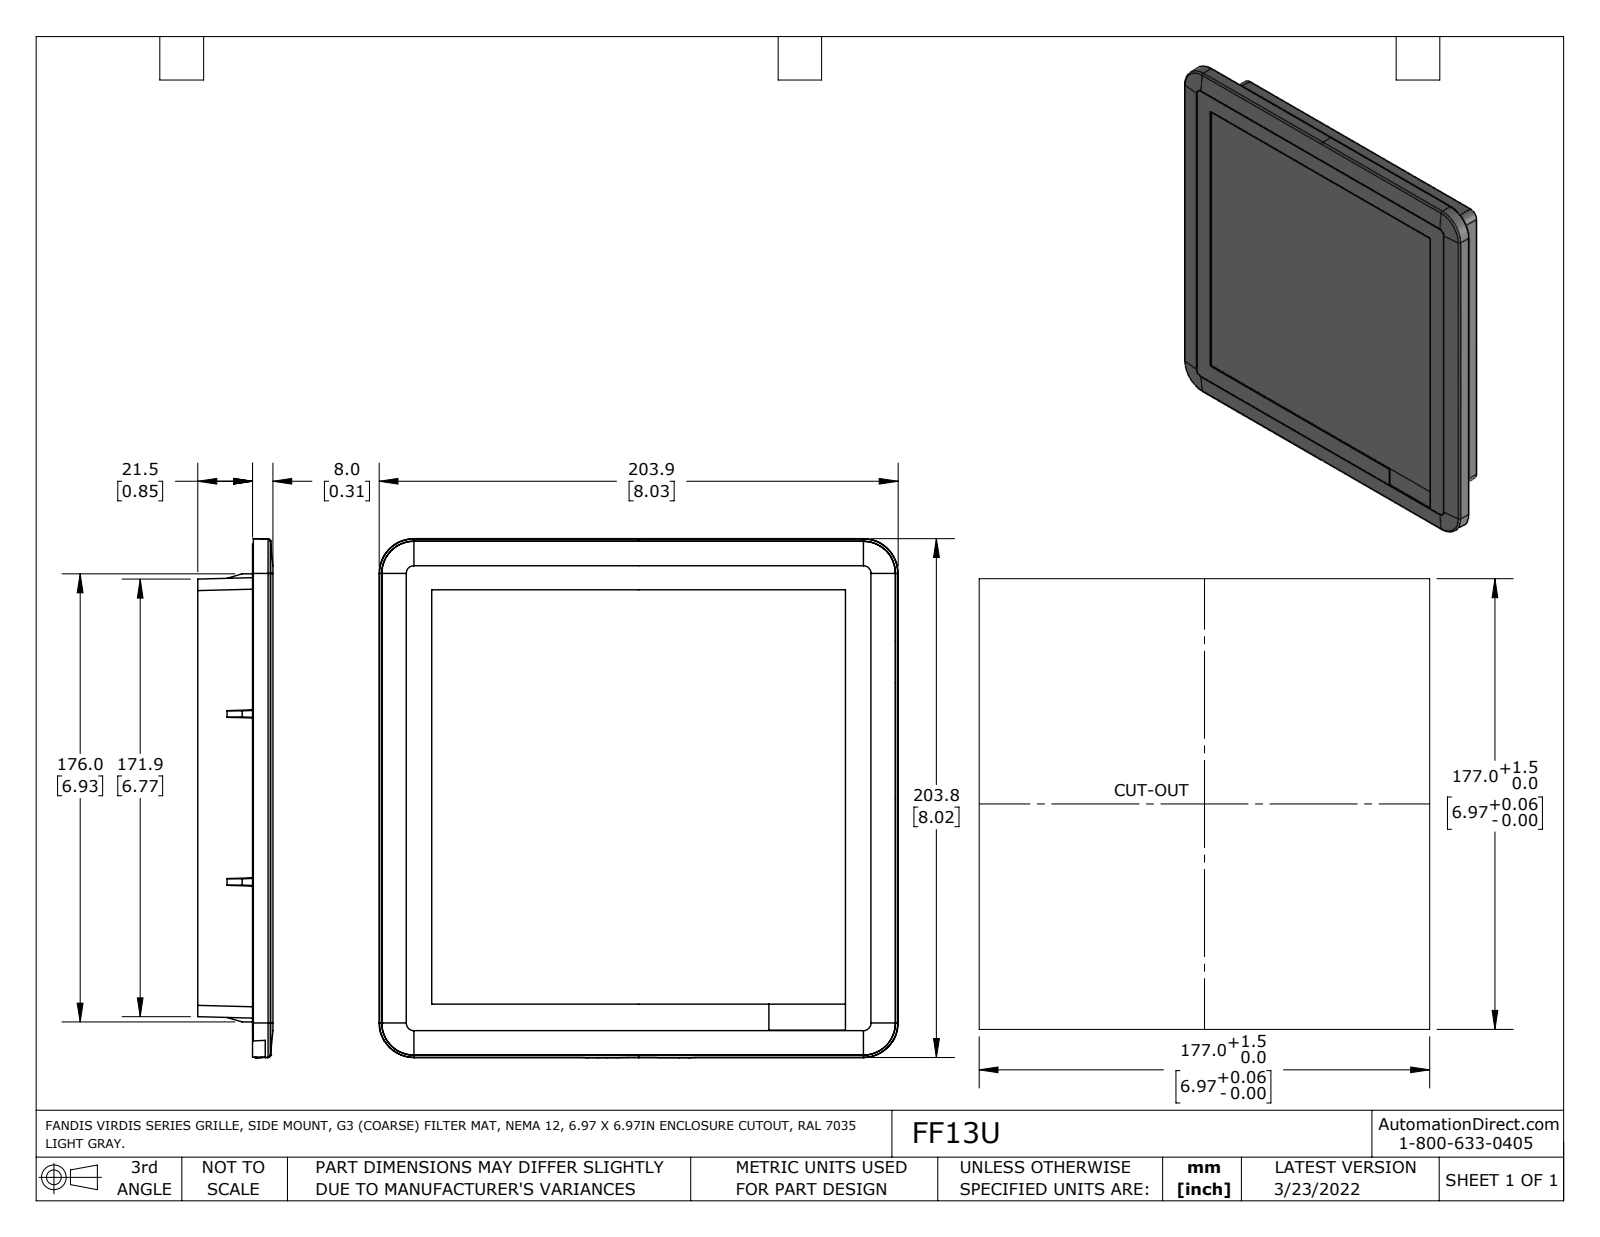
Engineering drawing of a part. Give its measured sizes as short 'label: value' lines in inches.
name: FF13y (p.c.)
written by: SolidWorks 2021 (AUTOMOTIVE_DESIGN)
unit: in
bodies: 1 solid, 241 faces (173 planar, 24 cylindrical, 44 other)
size: 8.028 × 8.027 × 1.161
volume: 57.71 in³; area: 171.1 in²
rounds: 8× R0.024, 4× R0.039, 4× R0.177, 4× R0.453, 2× R0.461
face distances: 1.142, 0.295, 0.846, 0.02, 0.315, 1.161, 0.236, 0.217, 0.079, 0.925
